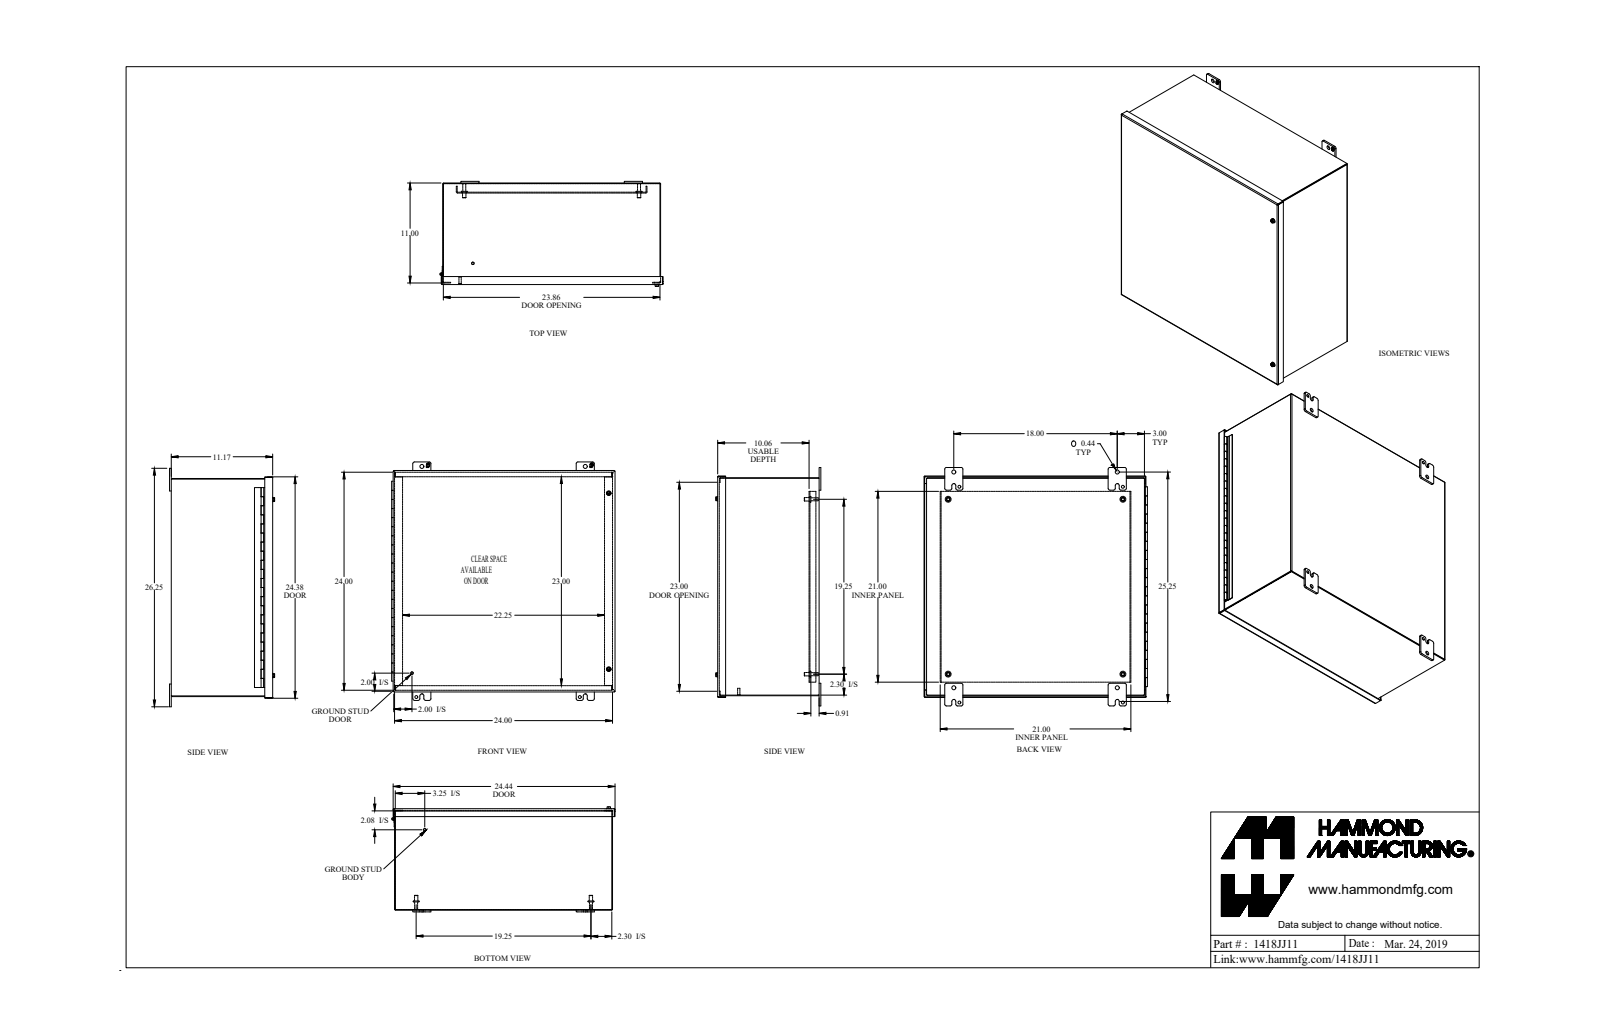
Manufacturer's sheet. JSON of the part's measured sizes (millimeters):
{"part_name": "1418JJ11_Default", "step_written_by": "SolidWorks 2018 (CONFIG_CONTROL_DESIGN)", "units": "millimeters", "bodies": {"solids": 34, "faces": 912, "planar": 561, "cylindrical": 309, "other": 42}, "overall_size": [666.8, 624.9, 293.9], "volume_mm3": 4043000, "surface_area_mm2": 3975000, "round_holes": [[8, 6], [11.1, 4], [12.7, 4], [6.6, 2], [6.8, 2], [7.1, 2], [7.4, 2], [7.8, 2], [10.1, 2], [4.7, 1], [11.3, 1], [11.3, 1]], "round_bosses_or_shafts": [[16.5, 4], [9.5, 4], [8.4, 4], [25.4, 2], [13, 2], [12.7, 2], [9.9, 2], [7.1, 2]], "partial_cylinders_radius": [[4.8, 24], [6.4, 20], [0.9, 10], [2.7, 10], [5.5, 8], [3.4, 6], [1.5, 5], [3.2, 4]], "face_to_face_distances": [1.8, 281.9, 283.8, 280.1, 607.8, 607.8, 2.4, 28, 26.2, 253.9], "hole_center_spacings": [489, 44.1, 457.2, 603.3, 756.9, 565.4, 1.5, 41.3]}
